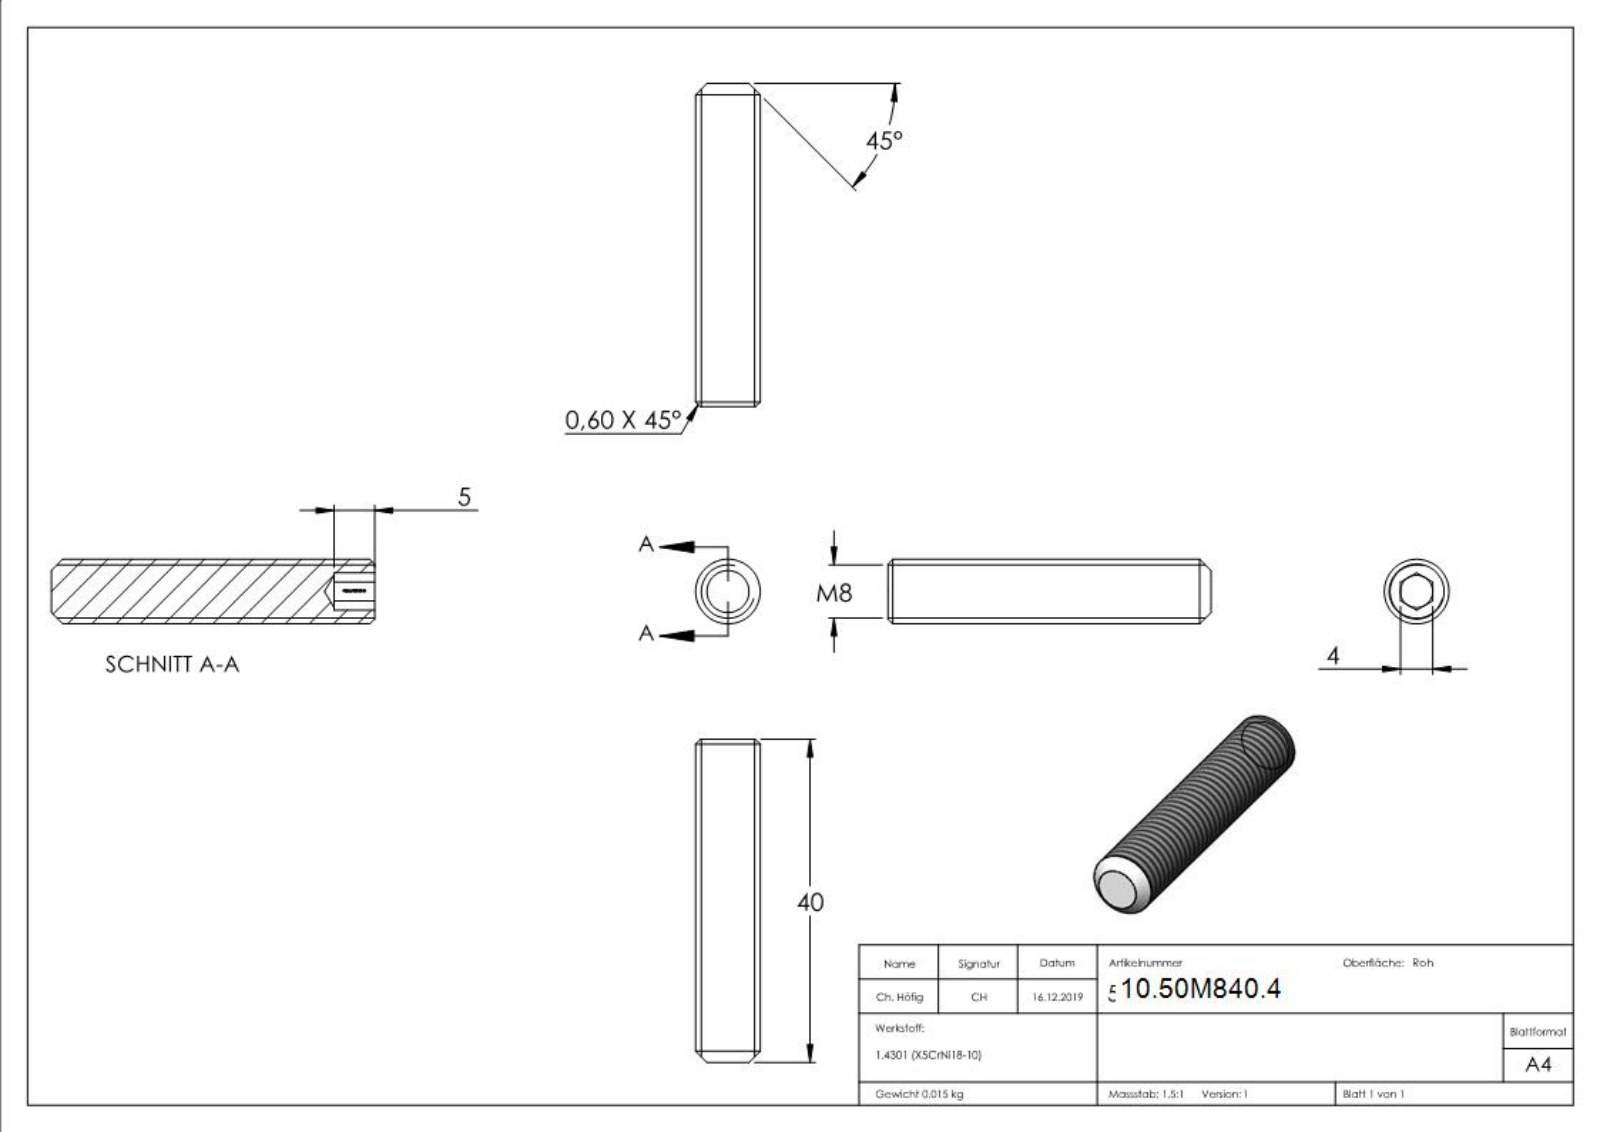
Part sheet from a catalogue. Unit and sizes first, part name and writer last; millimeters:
Units: millimetres
Overall size (bounding box): 70 × 8 × 8
Round bosses / shafts (diameter × count): ⌀8 ×1
Main face-to-face distances: 4, 40, 35, 5, 4.1, 0.48, 0.54, 1.67, 1.69, 0.34
Volume: 1 910 mm³ · Surface area: 1 146 mm²
Bodies: 1 solid, 295 faces (148 planar, 1 cylindrical, 146 other)
Part name (STEP PRODUCT): 58300-240-40
STEP written by: SolidWorks 2015 (CONFIG_CONTROL_DESIGN)
